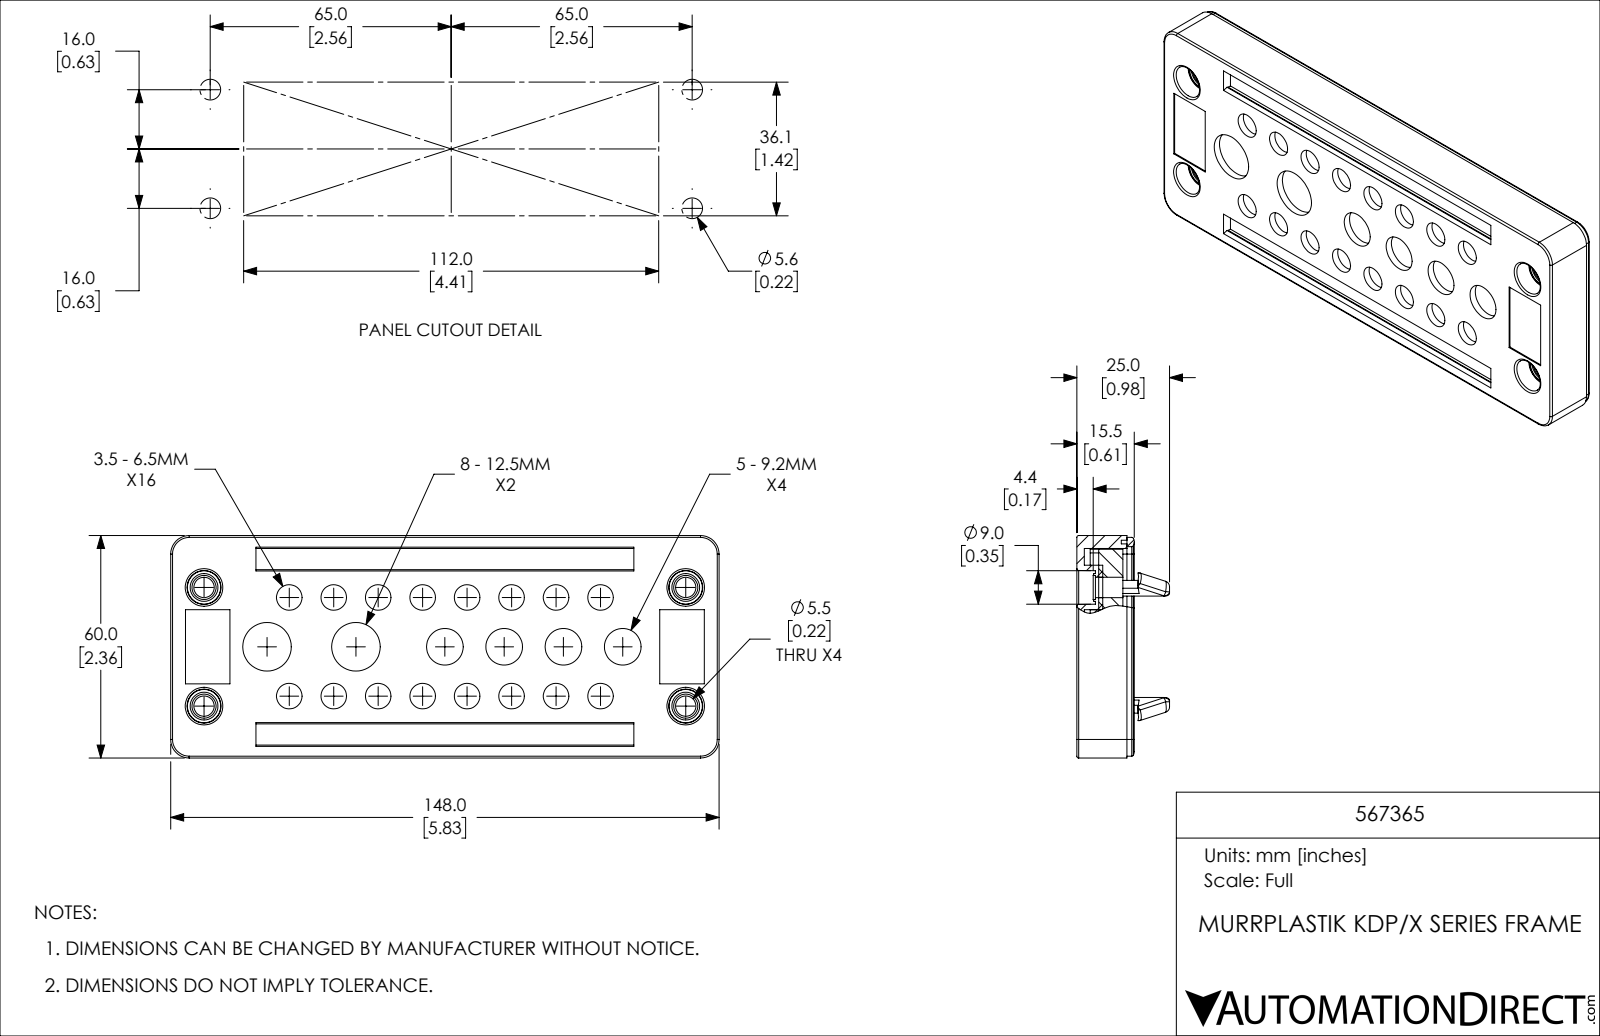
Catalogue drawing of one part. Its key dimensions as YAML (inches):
part_name: "567365"
step_written_by: "SolidWorks 2019 (CONFIG_CONTROL_DESIGN)"
units: inches
bodies: {solids: 4, faces: 458, planar: 162, cylindrical: 244, other: 52}
overall_size: [5.827, 2.362, 0.984]
volume: 4.906
surface_area: 102.3
round_holes:
  - {diameter: 0.272, count: 16}
  - {diameter: 0.413, count: 16}
  - {diameter: 0.217, count: 4}
  - {diameter: 0.256, count: 4}
  - {diameter: 0.39, count: 4}
  - {diameter: 0.543, count: 4}
  - {diameter: 0.516, count: 2}
  - {diameter: 0.657, count: 2}
round_bosses_or_shafts:
  - {diameter: 0.295, count: 4}
partial_cylinders:
  - {radius: 0.059, count: 20}
  - {radius: 0.02, count: 12}
  - {radius: 0.079, count: 12}
  - {radius: 0.039, count: 8}
  - {radius: 0.118, count: 8}
  - {radius: 0.108, count: 4}
  - {radius: 0.128, count: 4}
  - {radius: 0.138, count: 4}
face_to_face_distances: [0.091, 0.232, 0.142, 0.256, 0.488, 0.346, 0.079, 0.063, 0.154, 0.409]
hole_center_spacings: [0.472, 0.945, 1.417, 1.89, 1.402, 1.138, 2.362, 0.574]
